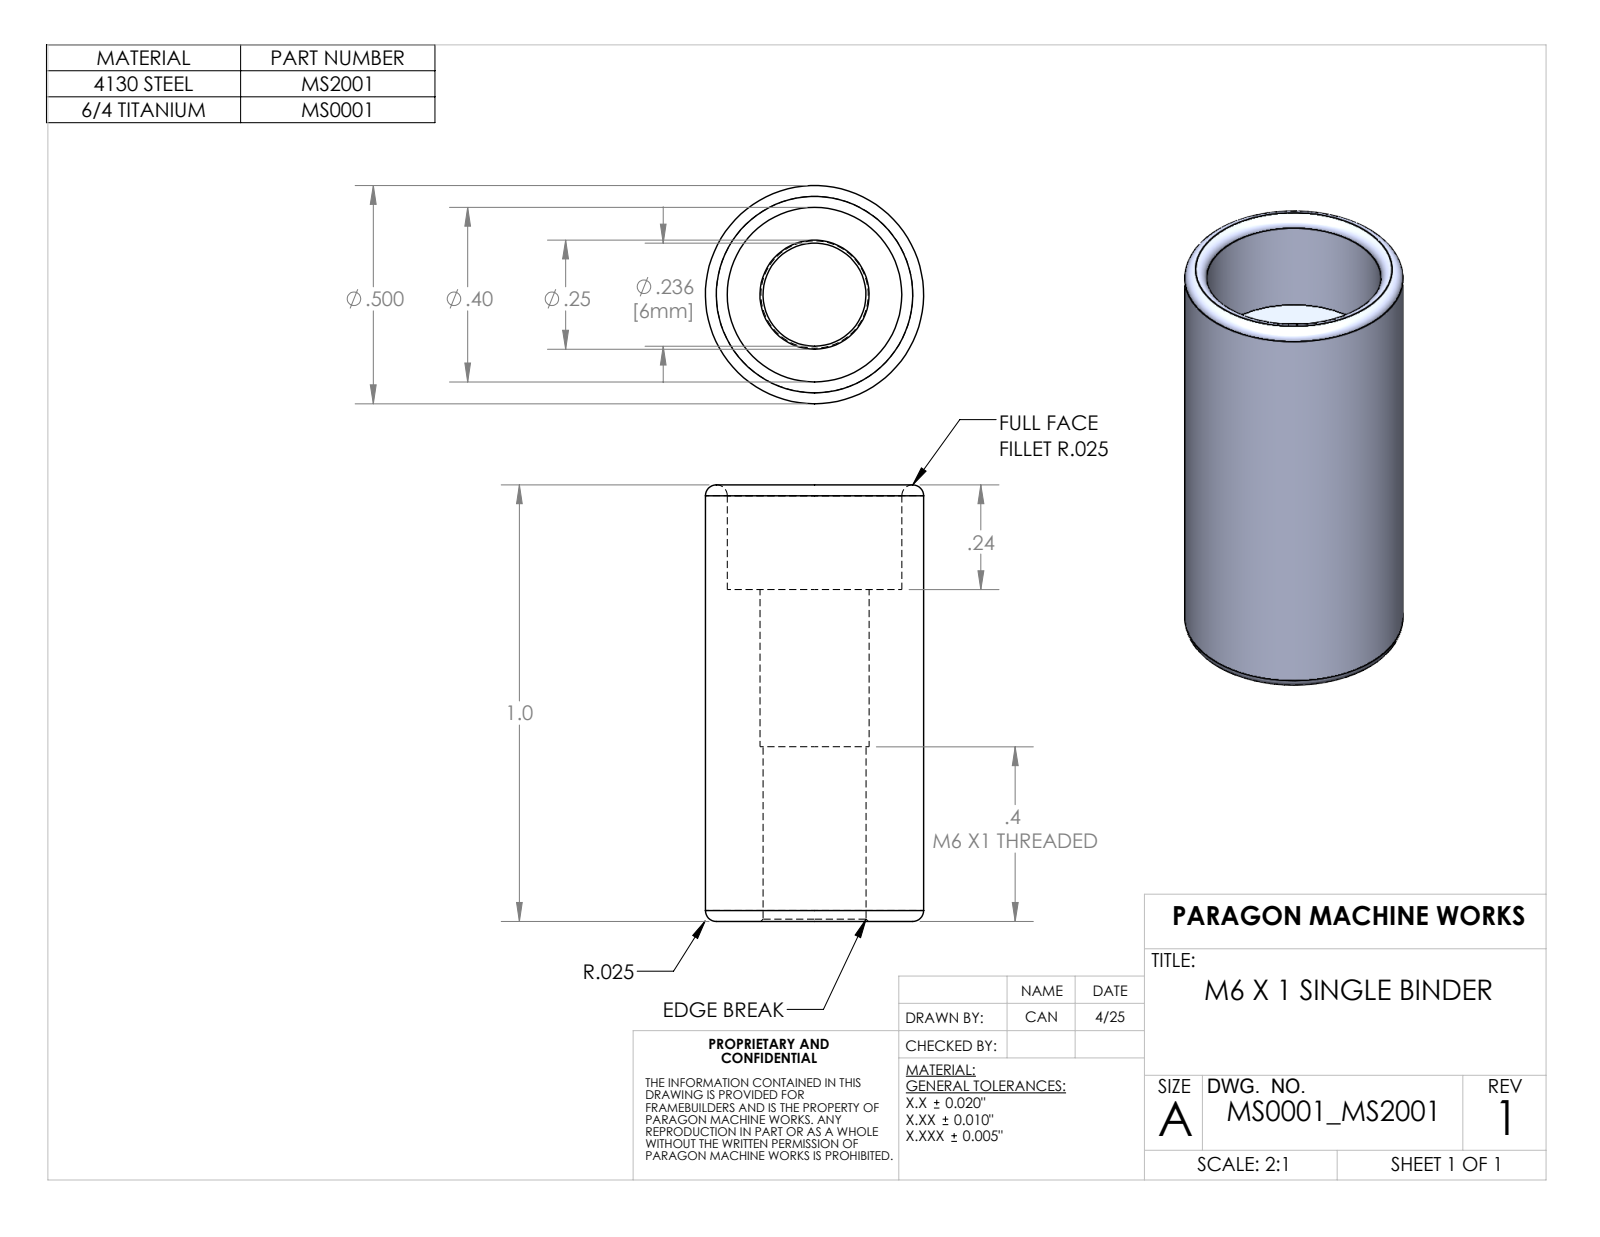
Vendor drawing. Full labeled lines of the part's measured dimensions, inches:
Part name (STEP PRODUCT): MS0001_MS2001
STEP written by: SolidWorks 2023 (AUTOMOTIVE_DESIGN)
Units: inches
Bodies: 1 solid, 19 faces (3 planar, 8 cylindrical, 8 other)
Overall size (bounding box): 1 × 0.5 × 0.5
Volume: 0.13 in³ · Surface area: 2.707 in²
Round holes (diameter × count): ⌀0.236 ×1, ⌀0.25 ×1, ⌀0.4 ×1
Round bosses / shafts (diameter × count): ⌀0.5 ×1
Main face-to-face distances: 0.76, 0.4, 0.36
